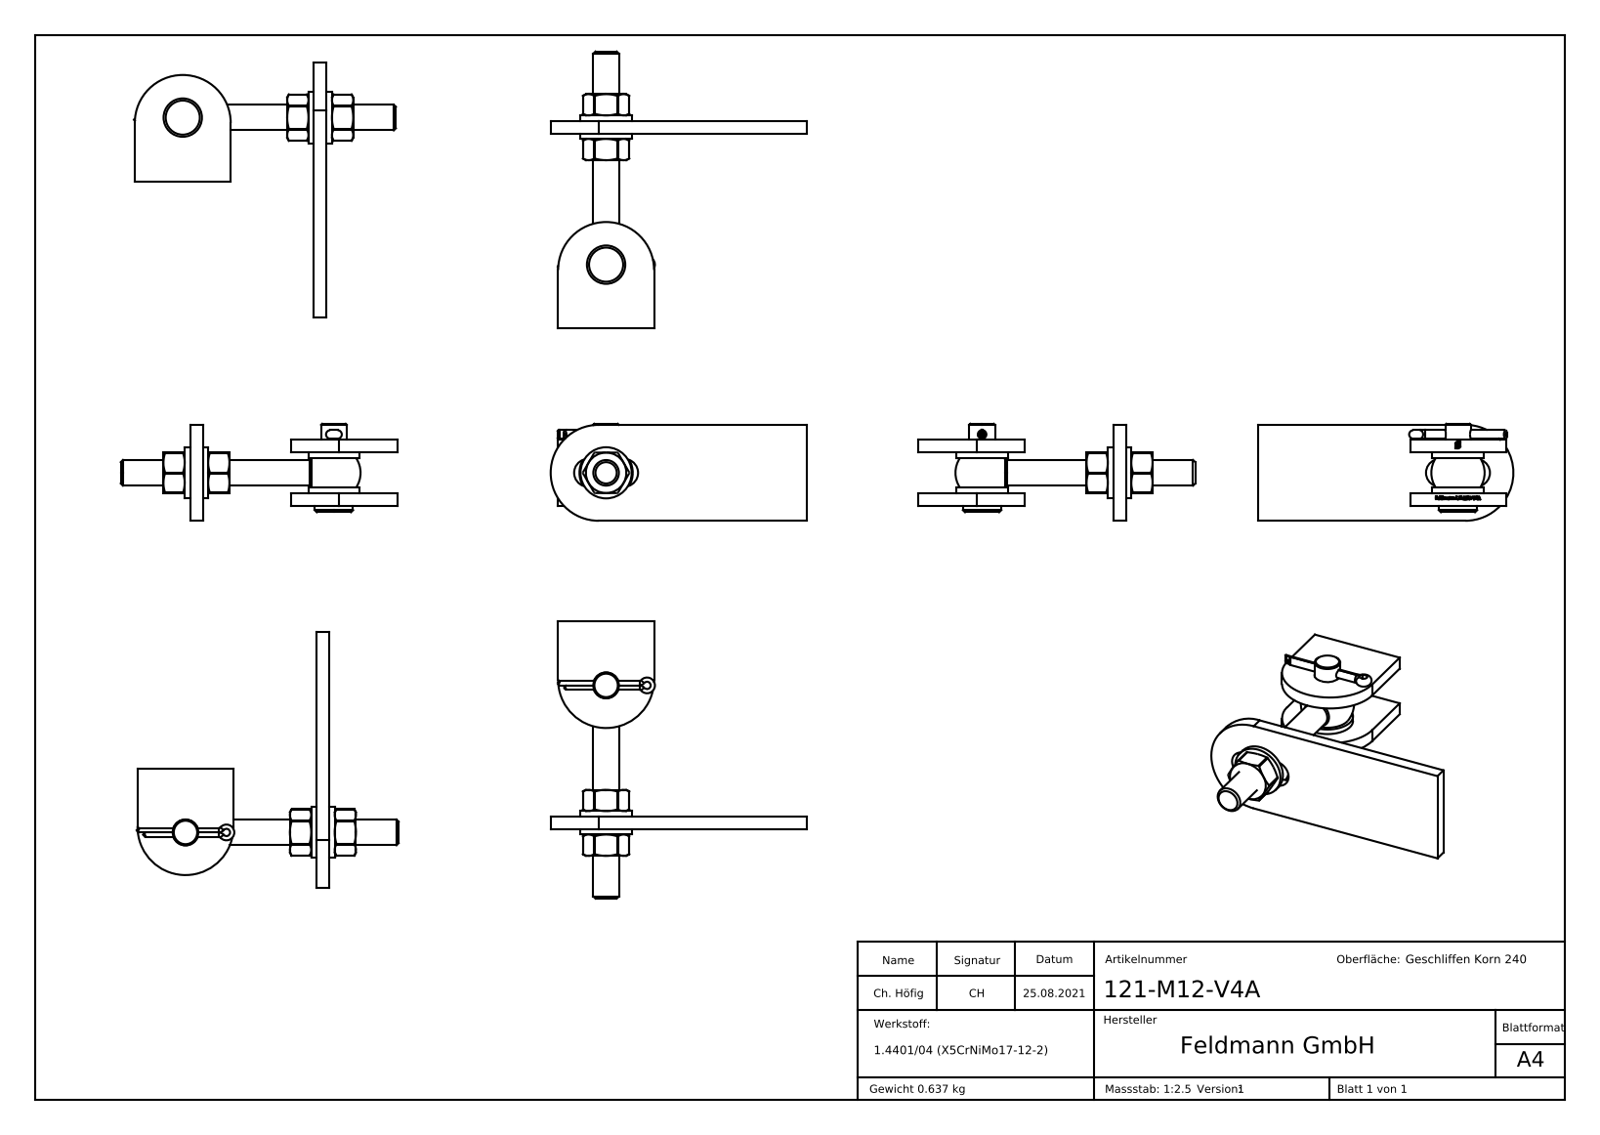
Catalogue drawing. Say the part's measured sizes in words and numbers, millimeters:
The part is named "Splint DIN94 - ISO 1234 Konfig_DIN 94 4x36; 121-MXX-XXX Teil4_121-M12-V4A Teil4; 121-MXX-XXX Teil5; DIN 934 M4-M20 (+8 more)". Its 3-D file was written by "SolidWorks 2018 (CONFIG_CONTROL_DESIGN)". It is 12 solids with 397 faces: 238 planar, 41 cylindrical and 118 other. Overall it measures 24000 by 14000.03 by 14000 millimeters. Its volume is 79 708 cubic millimeters and its surface area 37 184 square millimeters. Round holes: 2 of diameter 13, 1 of diameter 10.2, 1 of diameter 12.2. Round bosses or shafts: 2 of diameter 24, 2 of diameter 12, 1 of diameter 18, 1 of diameter 4. Partial cylindrical surfaces (rounded edges, fillets, slot ends): 6 of radius 0.5, 2 of radius 1, 2 of radius 2.99, 2 of radius 6.5, 2 of radius 22.5, 1 of radius 1.71. The main face-to-face distances are 6, 25, 19, 31, 2.5, 8.5, 13, 29.5, 16.5, 7.
